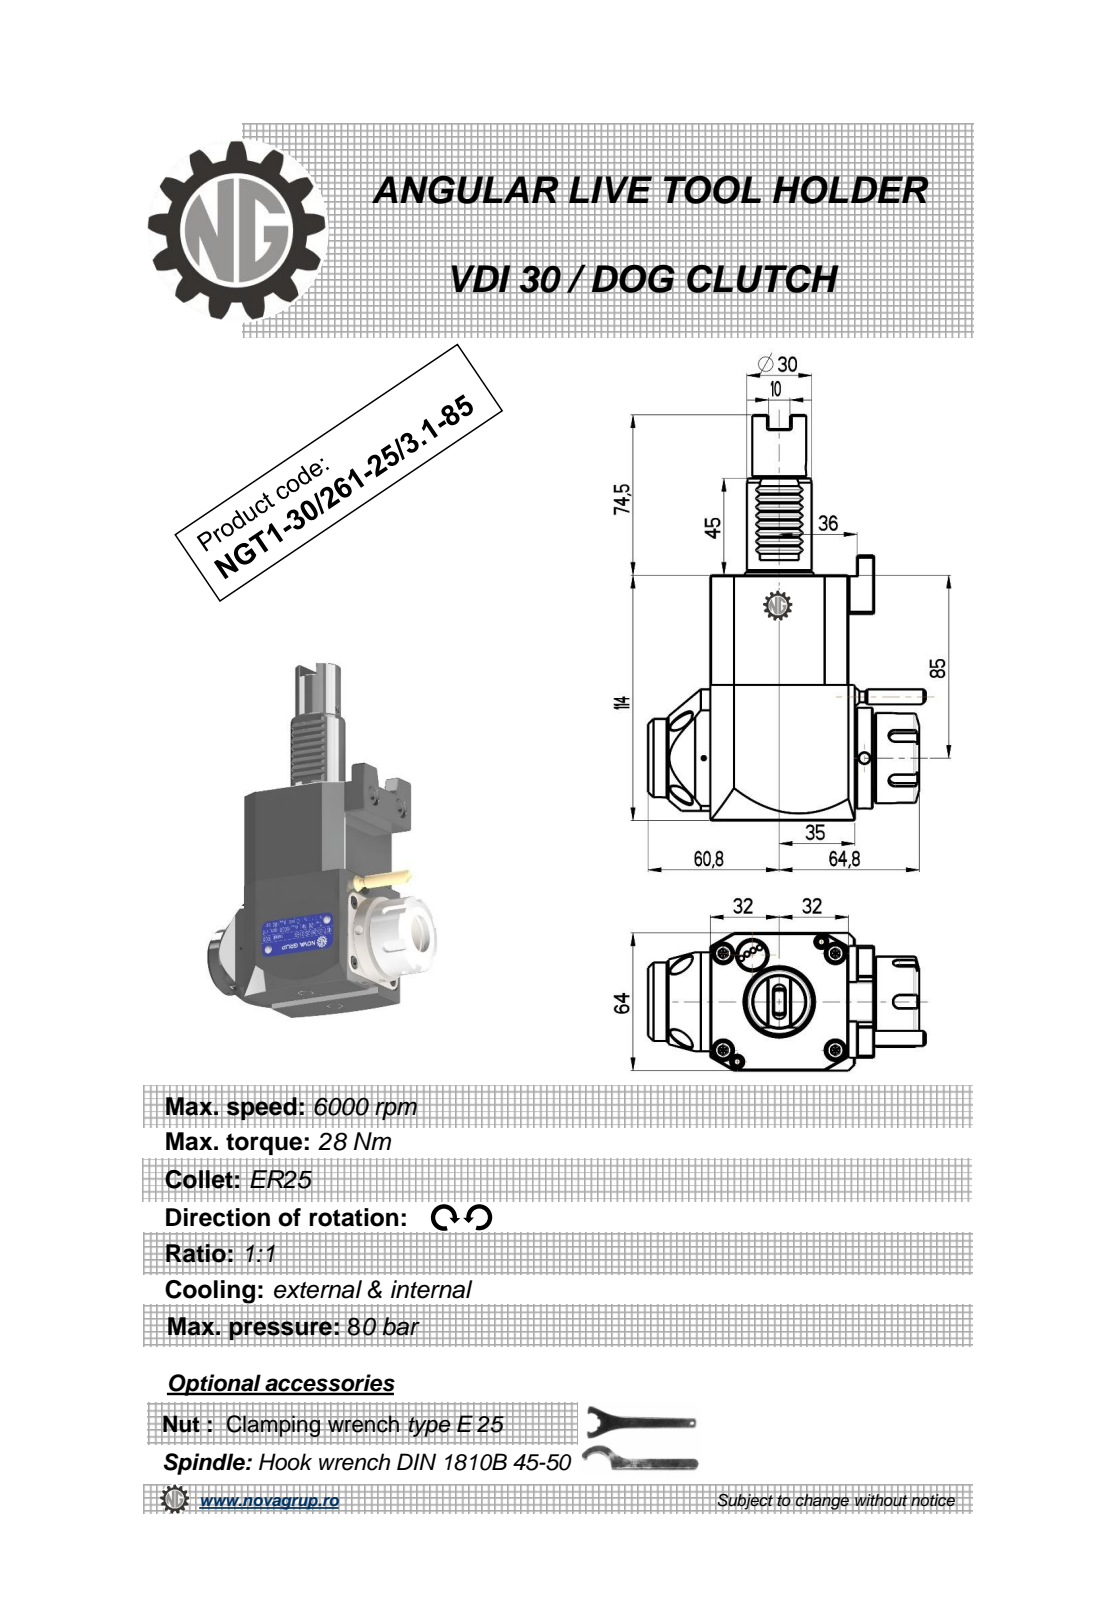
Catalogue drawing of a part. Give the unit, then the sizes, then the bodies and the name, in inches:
Units: inches
Overall size (bounding box): 7.421 × 5.064 × 2.52
Round holes (diameter × count): ⌀0.197 ×2, ⌀0.098 ×1, ⌀0.118 ×1, ⌀0.165 ×1, ⌀0.799 ×1
Round bosses / shafts (diameter × count): ⌀1.85 ×1, ⌀1.654 ×1, ⌀1.437 ×1, ⌀1.378 ×1, ⌀1.181 ×1, ⌀0.984 ×1, ⌀0.353 ×1, ⌀0.276 ×1
Partial cylindrical surfaces — rounded edges, fillets, slot ends (radius × count): R0.012 ×8, R0.01 ×6, R0.118 ×5, R0.02 ×2, R0.039 ×2, R6.299 ×2, R1.26 ×1
Main face-to-face distances: 2.52, 4.488, 0.354, 0.02, 0.118, 3.78, 2.646, 0.126, 3.009, 2.638
Hole centre spacings: 1.307, 4.246, 5.315
Volume: 37.1 in³ · Surface area: 89.35 in²
Bodies: 1 solid, 385 faces (191 planar, 64 cylindrical, 130 other)
Part name (STEP PRODUCT): NGT1_30_261_25_3_1_85
STEP written by: PRO/ENGINEER BY PARAMETRIC TECHNOLOGY CORPORATION, 2010280 (CONFIG_CONTROL_DESIGN)
